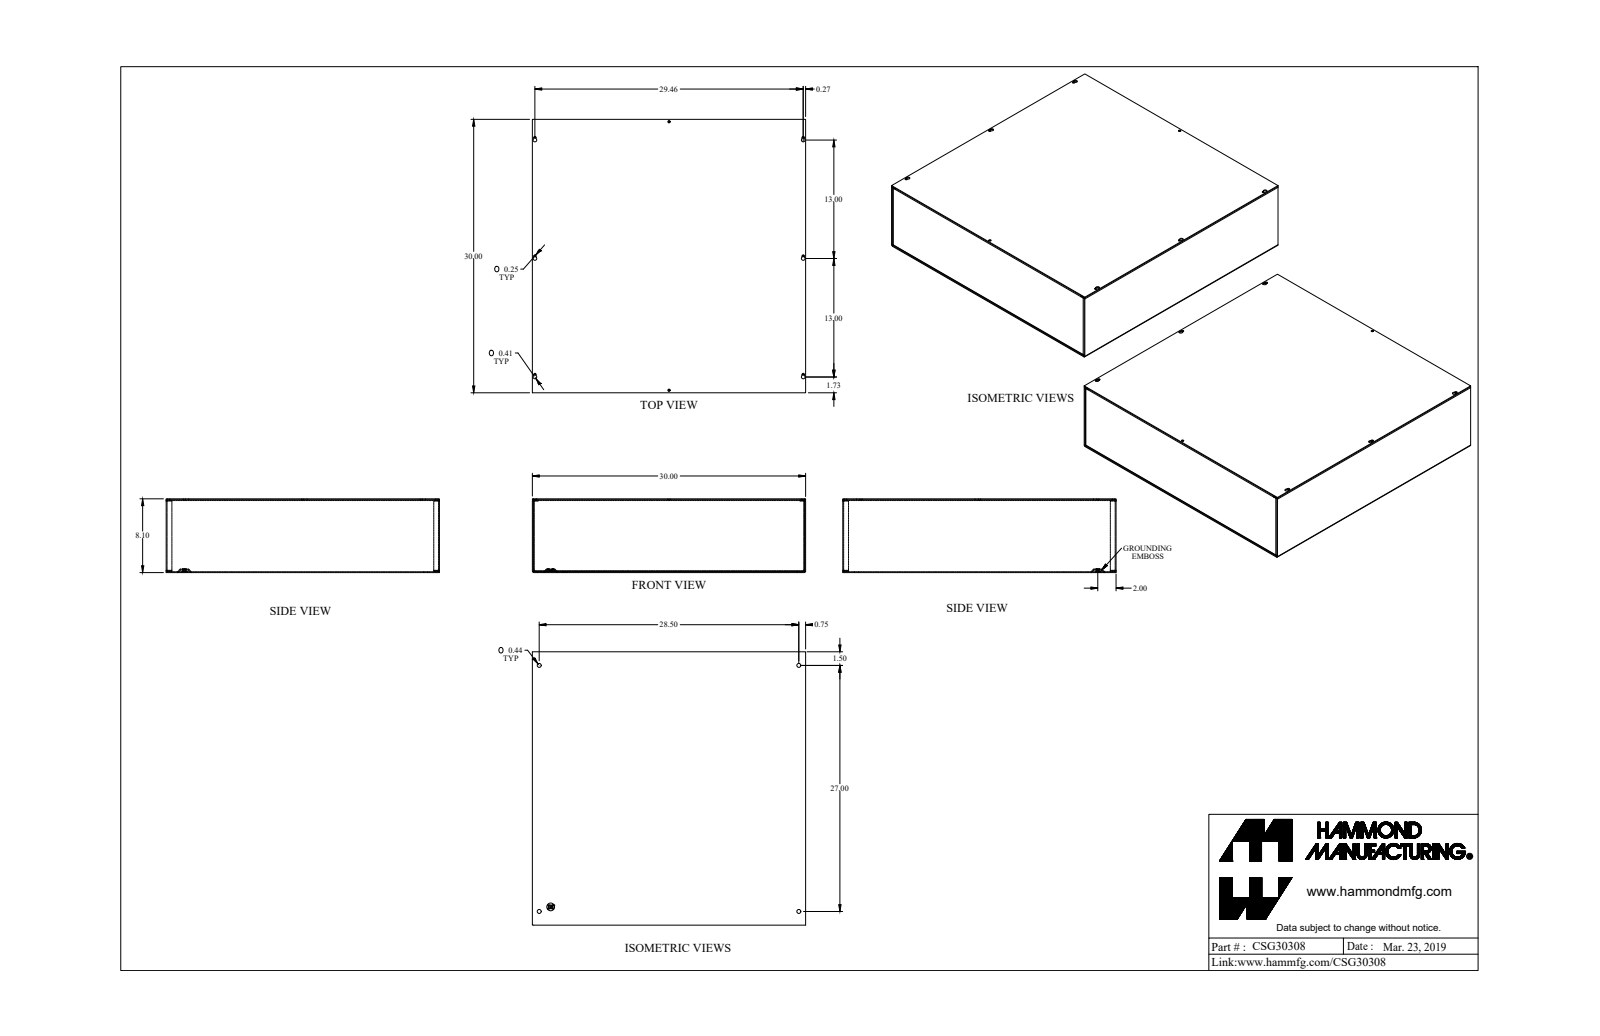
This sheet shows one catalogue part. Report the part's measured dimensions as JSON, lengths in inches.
{"part_name": "CSG30308_Default", "step_written_by": "SolidWorks 2019 (CONFIG_CONTROL_DESIGN)", "units": "inches", "bodies": {"solids": 4, "faces": 221, "planar": 121, "cylindrical": 92, "other": 8}, "overall_size": [30, 30, 8.095], "volume_in3": 268.5, "surface_area_in2": 5696, "round_holes": [[0.17, 9], [0.437, 4], [0.25, 2], [0.5, 1]], "round_bosses_or_shafts": [[0.492, 1], [0.36, 1]], "partial_cylinders_radius": [[0.048, 12], [0.143, 12], [0.095, 8], [0.125, 6], [0.203, 6]], "face_to_face_distances": [0.095, 8, 7.905, 29.905, 8.095, 30, 29.81, 0.19, 7.81, 0.105], "hole_center_spacings": [0.693, 13, 13.509, 14.303, 14.831, 20.831, 26.504, 28.984]}
